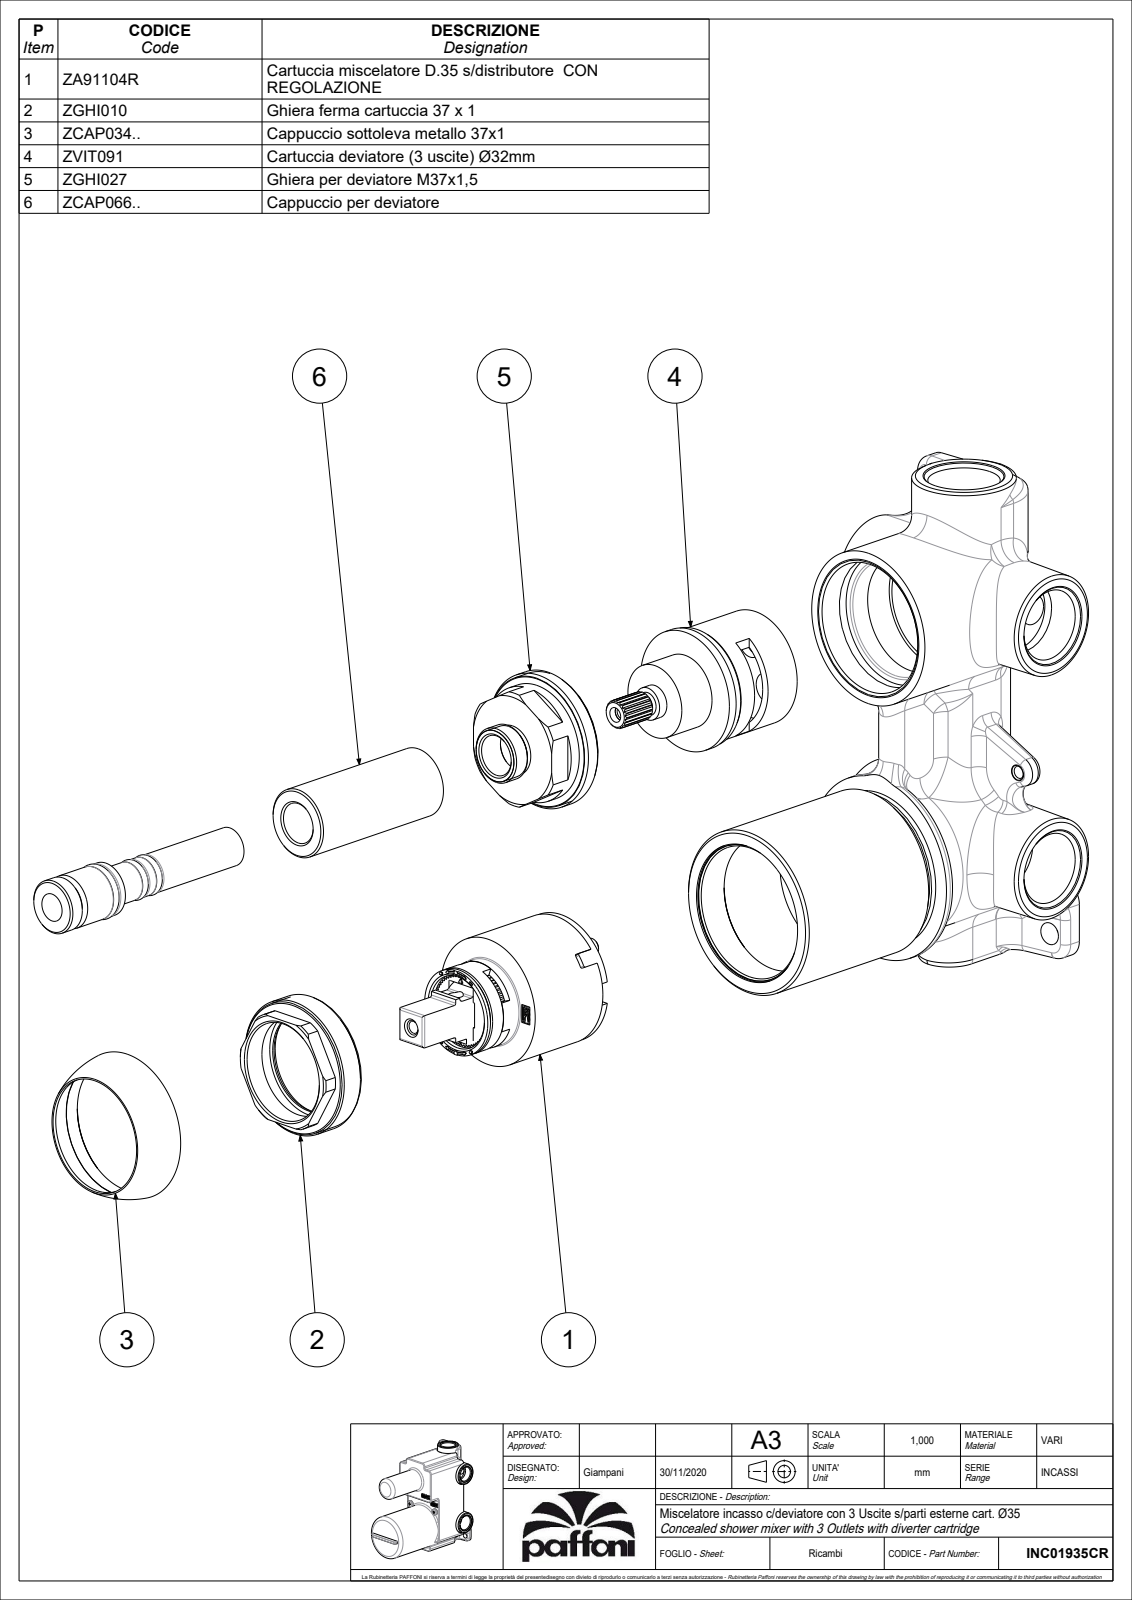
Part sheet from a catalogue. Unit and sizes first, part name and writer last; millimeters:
Units: millimetres
Overall size (bounding box): 137 × 135.5 × 66
Round holes (diameter × count): ⌀8 ×7, ⌀7 ×6, ⌀6 ×3, ⌀8.2 ×3, ⌀9.5 ×3, ⌀19 ×3, ⌀4 ×2, ⌀11 ×2, ⌀3.3 ×1, ⌀4.2 ×1, ⌀5 ×1, ⌀8.5 ×1
Round bosses / shafts (diameter × count): ⌀12 ×3, ⌀42 ×2, ⌀10.5 ×2, ⌀8 ×2, ⌀7.8 ×2, ⌀7.5 ×2, ⌀4 ×2, ⌀57 ×1
Partial cylindrical surfaces — rounded edges, fillets, slot ends (radius × count): R0.5 ×35, R1 ×34, R2 ×25, R4 ×18, R5 ×16, R0.15 ×11, R1.5 ×8, R3 ×8
Main face-to-face distances: 2, 56, 58, 55, 54, 8, 12.5, 16.5, 4, 57
Hole centre spacings: 5, 7.39, 8.6, 9.94, 12.81, 14.33, 57.16, 62.1
Volume: 311 128 mm³ · Surface area: 167 310 mm²
Bodies: 2 solids, 1928 faces (792 planar, 474 cylindrical, 662 other)
Part name (STEP PRODUCT): INC01935CR
STEP written by: CREO PARAMETRIC BY PTC INC, 2020044 (CONFIG_CONTROL_DESIGN)
